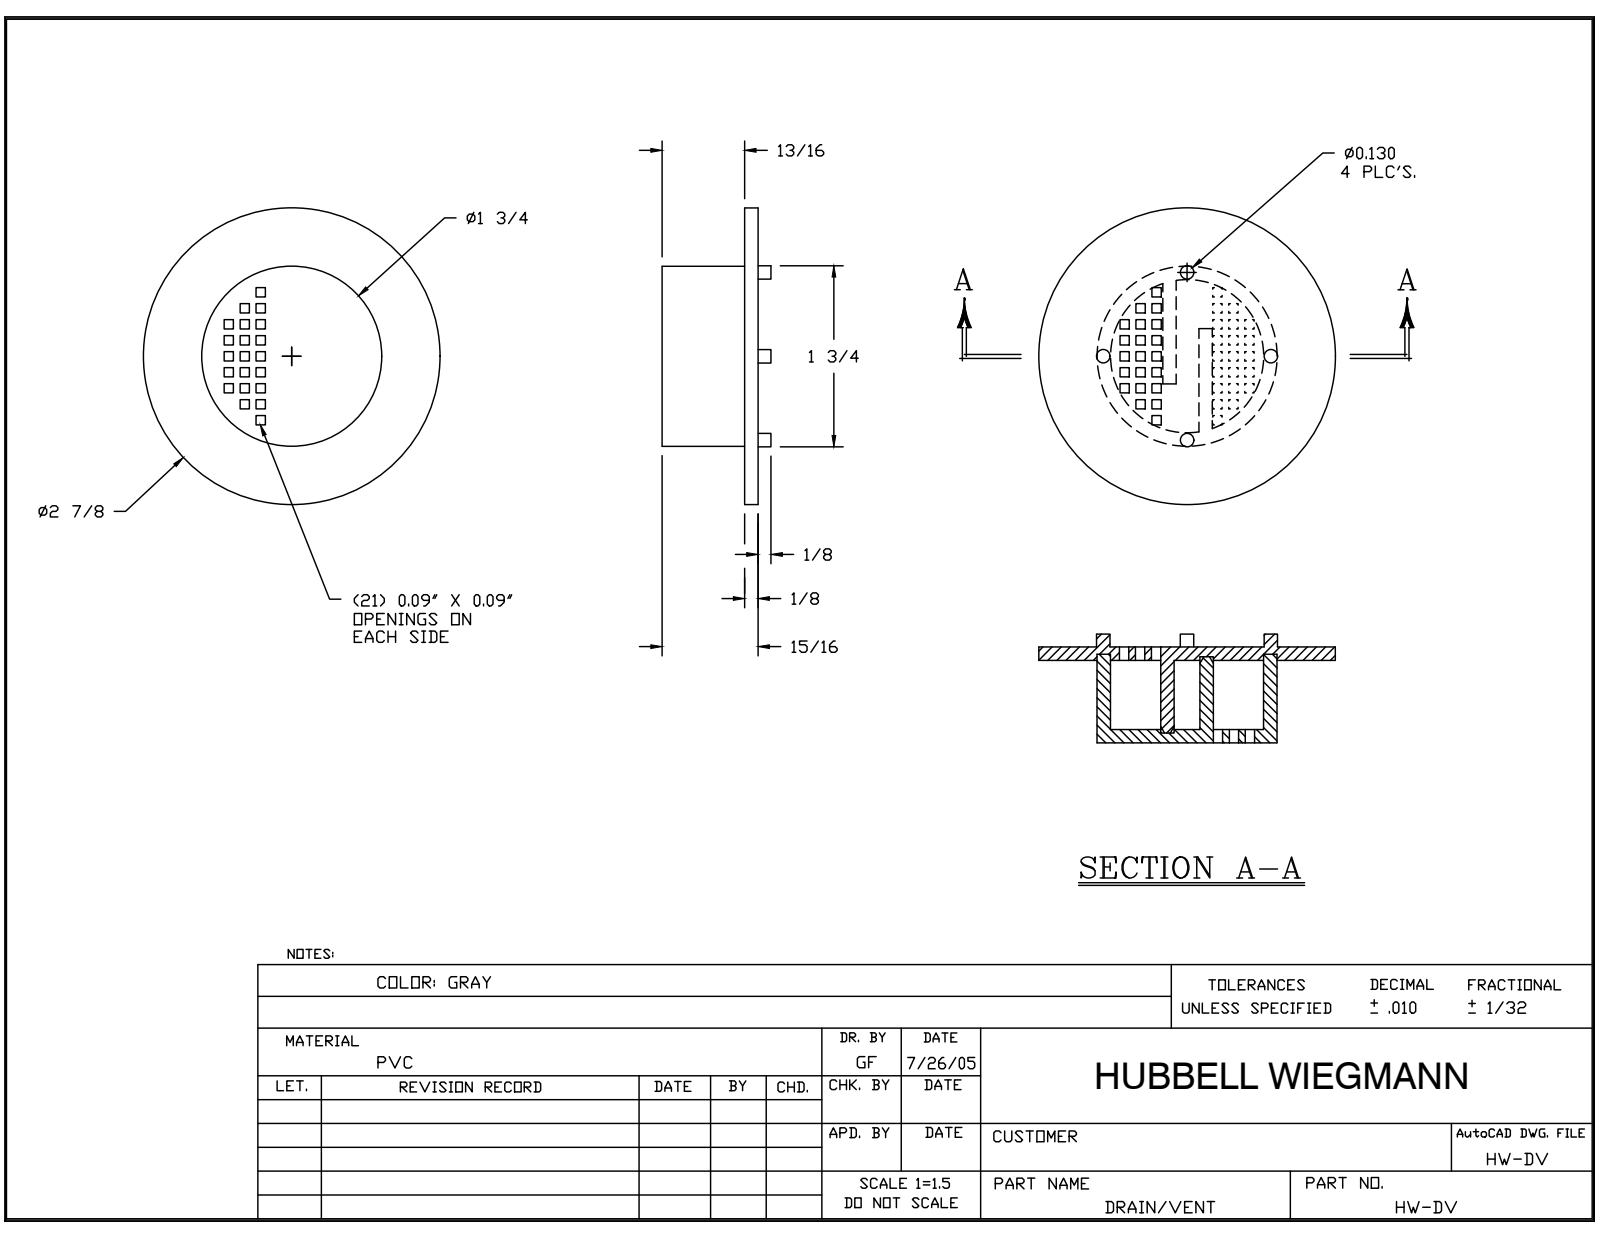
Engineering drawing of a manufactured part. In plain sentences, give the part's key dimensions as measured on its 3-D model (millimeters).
The part is named "PARTA; PARTB; DV1PVC_STP". Its 3-D file was written by "Autodesk Inventor 2014 (AUTOMOTIVE_DESIGN)". It is 2 solids with 199 faces: 190 planar, 9 cylindrical and 0 other. Overall it measures 57.15 by 57.15 by 25.4 millimeters. Its volume is 21 697 cubic millimeters and its surface area 16 751 square millimeters. Round holes: 1 of diameter 38.1, 1 of diameter 44.45. Round bosses or shafts: 4 of diameter 3.17, 1 of diameter 57.15. The main face-to-face distances are 3.17, 19.05, 22.22, 15.88, 17.46, 1.59, 1.58, 3.18, 20.63, 0.79.
